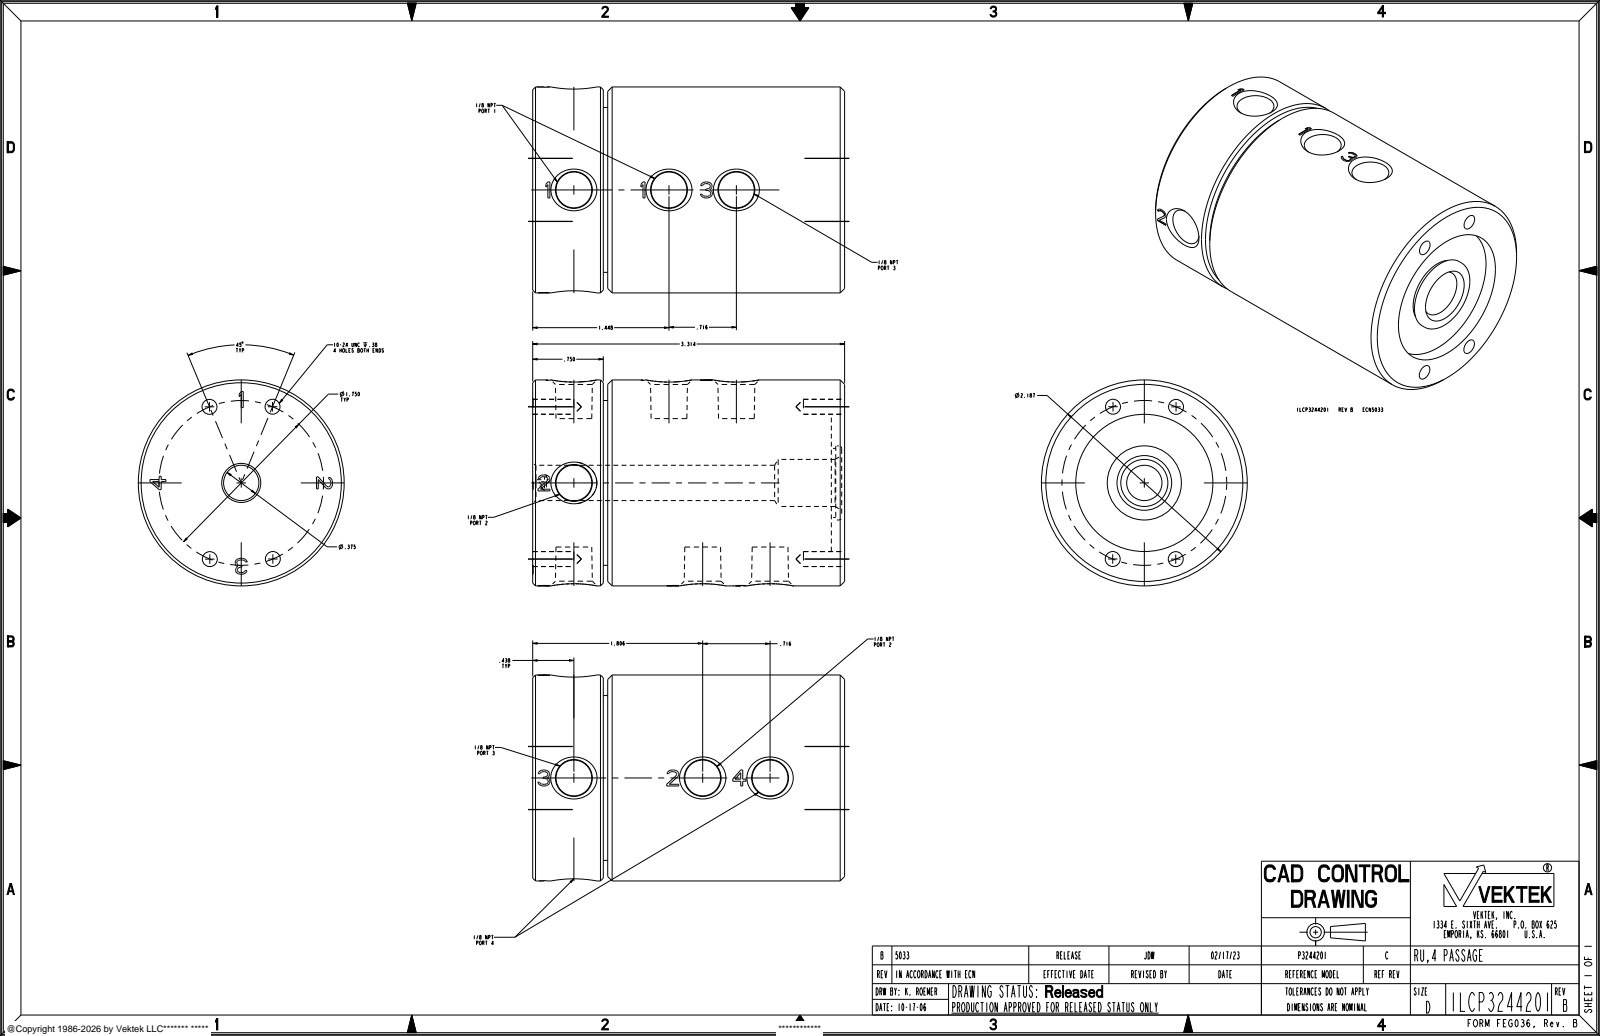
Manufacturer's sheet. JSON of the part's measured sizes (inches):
{"part_name": "ILCP3244201", "step_written_by": "CREO PARAMETRIC BY PTC INC, 2021164 (AUTOMOTIVE_DESIGN)", "units": "inches", "bodies": {"solids": 1, "faces": 462, "planar": 346, "cylindrical": 50, "other": 66}, "overall_size": [3.314, 2.187, 2.187], "volume_in3": 11.29, "surface_area_in2": 42.59, "round_holes": [[0.159, 4], [0.375, 1], [0.5, 1], [1.457, 1]], "round_bosses_or_shafts": [[2.187, 1], [1.75, 1], [0.787, 1], [0.733, 1]], "face_to_face_distances": [3.314, 0.141, 3.173, 0.75, 2.423, 2.564, 0.797, 0.047, 2.376, 2.517], "hole_center_spacings": [0.67, 0.875, 0.875, 1.617, 1.75, 1.75]}
